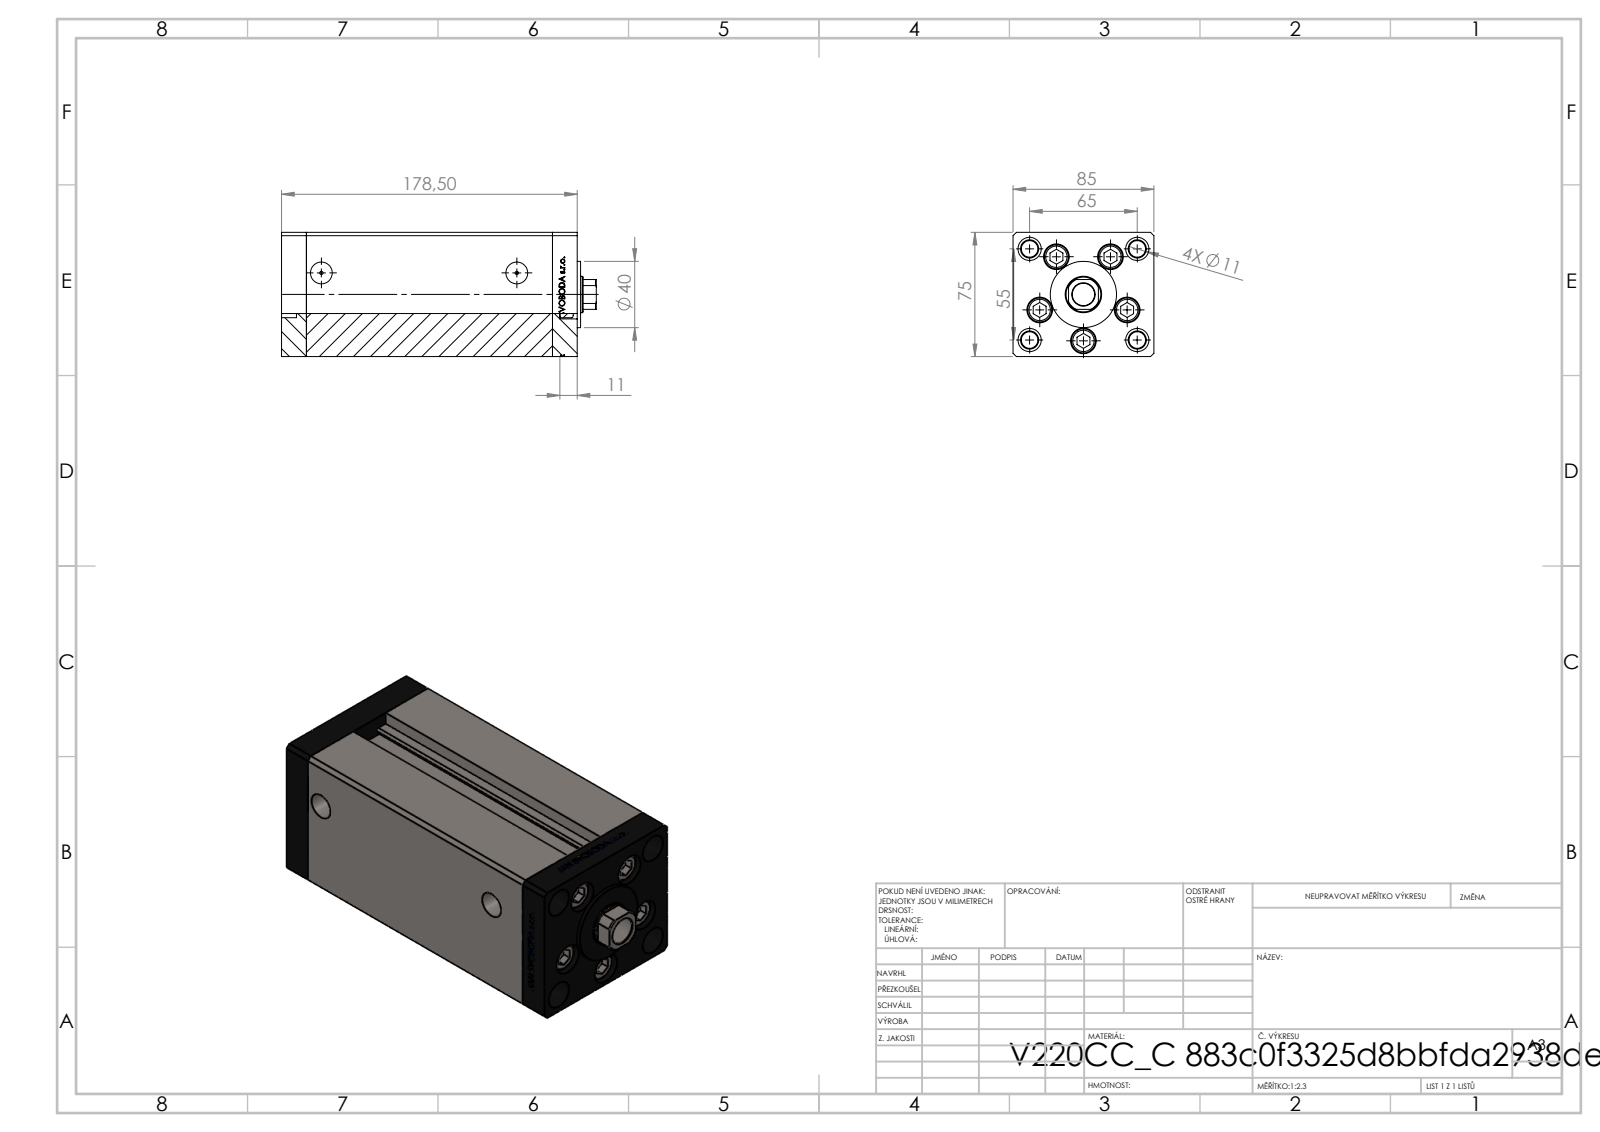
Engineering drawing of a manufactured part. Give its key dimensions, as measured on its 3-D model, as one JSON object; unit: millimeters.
{"part_name": "V220C FRONT; ALLEN BOLT; V220C BACK_C; V220C_C MIDDLE (+1 more)", "step_written_by": "SolidWorks 2019 (CONFIG_CONTROL_DESIGN)", "units": "millimeters", "bodies": {"solids": 13, "faces": 1171, "planar": 542, "cylindrical": 167, "other": 462}, "overall_size": [190, 85, 75], "volume_mm3": 945382, "surface_area_mm2": 180492, "round_holes": [[11, 9], [15.5, 5], [10, 4], [14, 4], [2, 2], [13.16, 2], [13.5, 1], [14.5, 1], [22, 1]], "round_bosses_or_shafts": [[8, 5], [14.5, 4], [40, 1]], "partial_cylinders_radius": [[0.93, 2], [10.5, 1]], "face_to_face_distances": [85, 75, 15, 148.5, 163.5, 10.5, 178.5, 34.25, 144.25, 129.25], "hole_center_spacings": [28, 42.57, 16.86, 19.17, 32.33, 32.5, 33.63, 37.33]}
